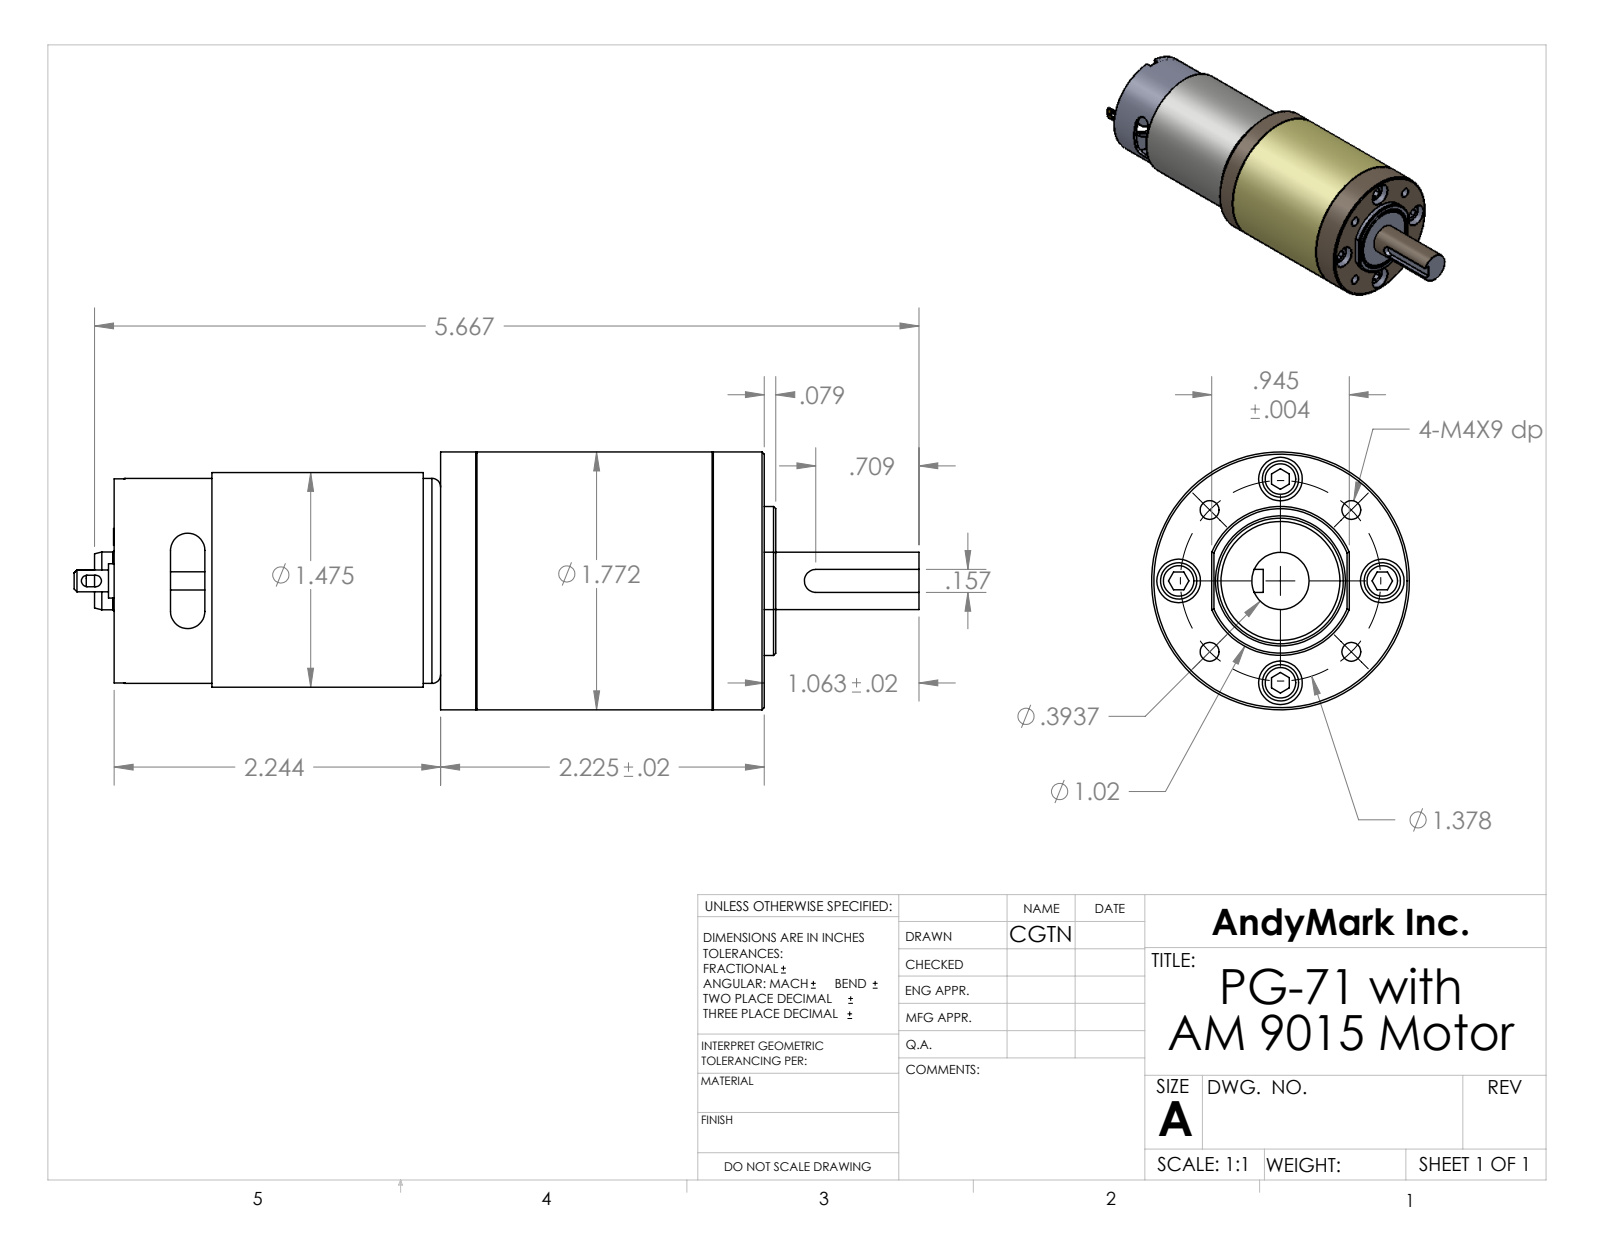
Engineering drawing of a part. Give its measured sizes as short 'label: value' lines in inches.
name: AM-0912 end cap; AM-0912 shield; AM-0912 red dot; AM-0912 armature (+8 more)
written by: SolidWorks 2010 (CONFIG_CONTROL_DESIGN)
unit: in
bodies: 13 solids, 590 faces (347 planar, 175 cylindrical, 68 other)
size: 5.808 × 1.772 × 1.772
volume: 6.546 in³; area: 65.16 in²
holes: 6× ⌀0.098, 4× ⌀0.13, 4× ⌀0.3, 2× ⌀0.098, 1× ⌀0.079, 1× ⌀0.125, 1× ⌀0.318, 1× ⌀0.4, 1× ⌀0.432, 1× ⌀0.864, 1× ⌀1.329, 1× ⌀1.369
bosses: 4× ⌀0.25, 3× ⌀0.115, 2× ⌀0.15, 2× ⌀0.115, 1× ⌀1.772, 1× ⌀1.489, 1× ⌀1.364, 1× ⌀1.326
rounds: 8× R0.02, 8× R0.08, 4× R0.039, 4× R0.053, 4× R0.06, 2× R0.118, 1× R0.079, 1× R0.326
face distances: 0.04, 2.164, 0.1, 1.14, 1.04, 3.365, 3.265, 2.225, 2.124, 1.064
hole spacings: 0.302, 0.372, 0.531, 0.532, 0.57, 0.626, 0.7, 0.856
